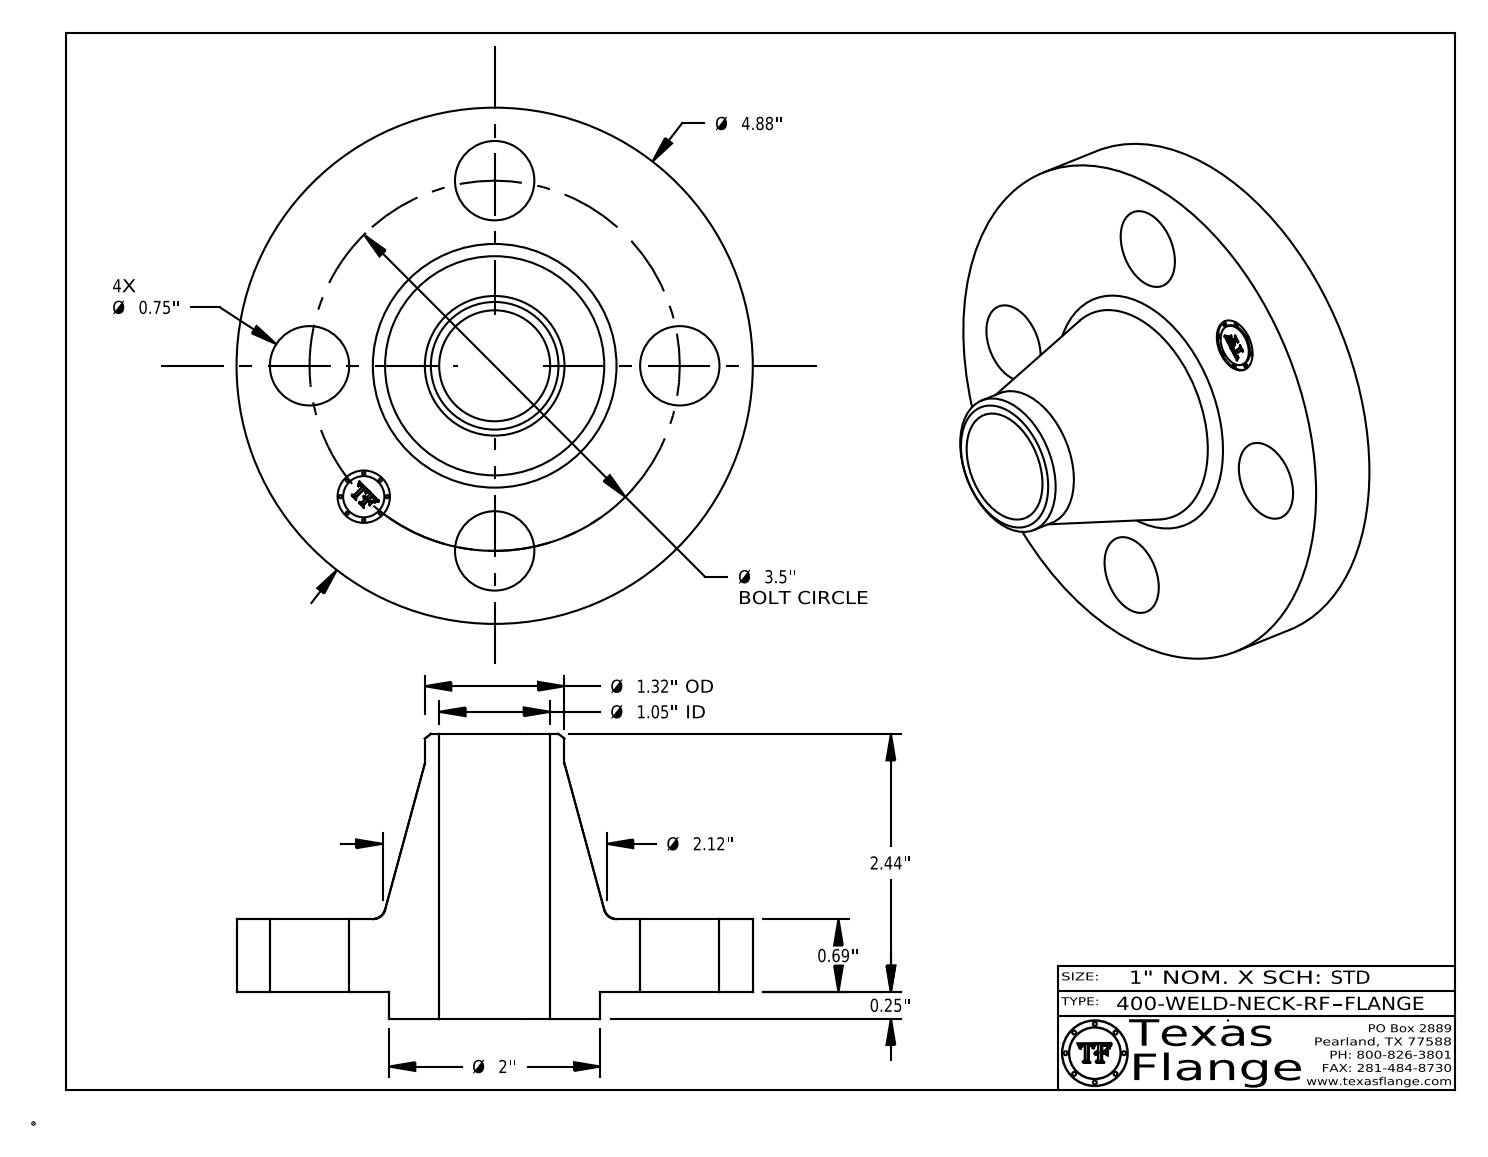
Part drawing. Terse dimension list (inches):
name: 400-WELD-NECK-RF
written by: CATIA V5 STEP AP214 (AUTOMOTIVE_DESIGN)
unit: in
bodies: 1 solid, 411 faces (369 planar, 36 cylindrical, 6 other)
size: 4.88 × 4.88 × 2.69
volume: 14.01 in³; area: 66.69 in²
holes: 4× ⌀0.75, 1× ⌀0.495, 1× ⌀1.049
bosses: 8× ⌀0.03, 1× ⌀4.88, 1× ⌀2, 1× ⌀1.32, 1× ⌀0.39
face distances: 0.69, 0.25, 0.94, 2.69, 2.44, 1.75, 0.015, 0.925, 0.675, 1.765
hole spacings: 1.75, 2.475, 1.339, 3.233, 3.5
